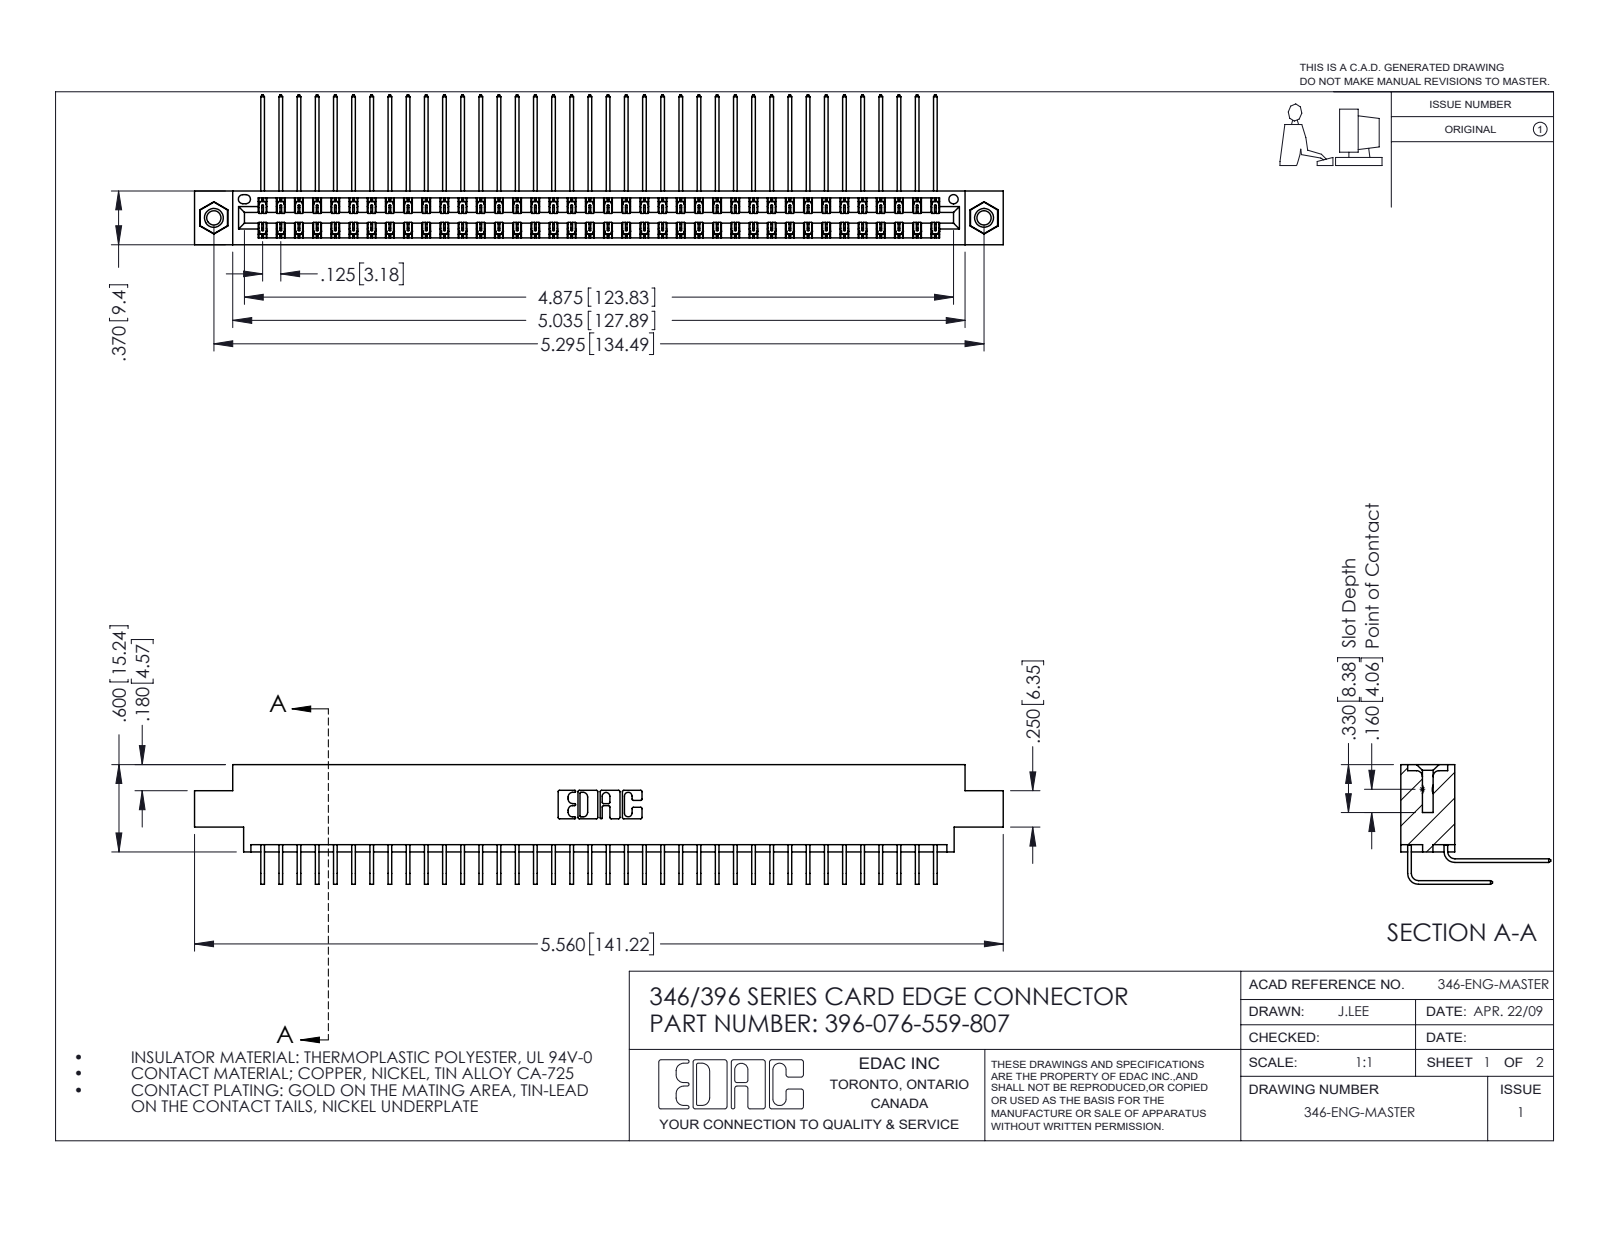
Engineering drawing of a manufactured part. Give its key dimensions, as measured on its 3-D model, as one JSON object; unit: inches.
{"part_name": "396-076-559-807; 345-250-001_345-250-005-103; 345-292-001_559 Tail - 2; 345-292-001_558 559 Tail - 1 (+1 more)", "step_written_by": "SolidWorks 2016 (CONFIG_CONTROL_DESIGN)", "units": "inches", "bodies": {"solids": 79, "faces": 4290, "planar": 2924, "cylindrical": 1350, "other": 16}, "overall_size": [5.56, 1.03, 0.823], "volume_in3": 0.855, "surface_area_in2": 33.34, "round_holes": [[0.098, 2], [0.125, 2], [0.156, 2], [0.064, 1]], "round_bosses_or_shafts": [[0.155, 2]], "partial_cylinders_radius": [[0.006, 114], [0.01, 22], [0.007, 6], [0.031, 6], [0.026, 3], [0.014, 2], [0.022, 2], [0.024, 2]], "face_to_face_distances": [0.048, 0.322, 0.025, 0.37, 0.25, 0.072, 0.298, 0.275, 0.222, 0.148], "hole_center_spacings": [0.246, 5.086, 5.295]}
